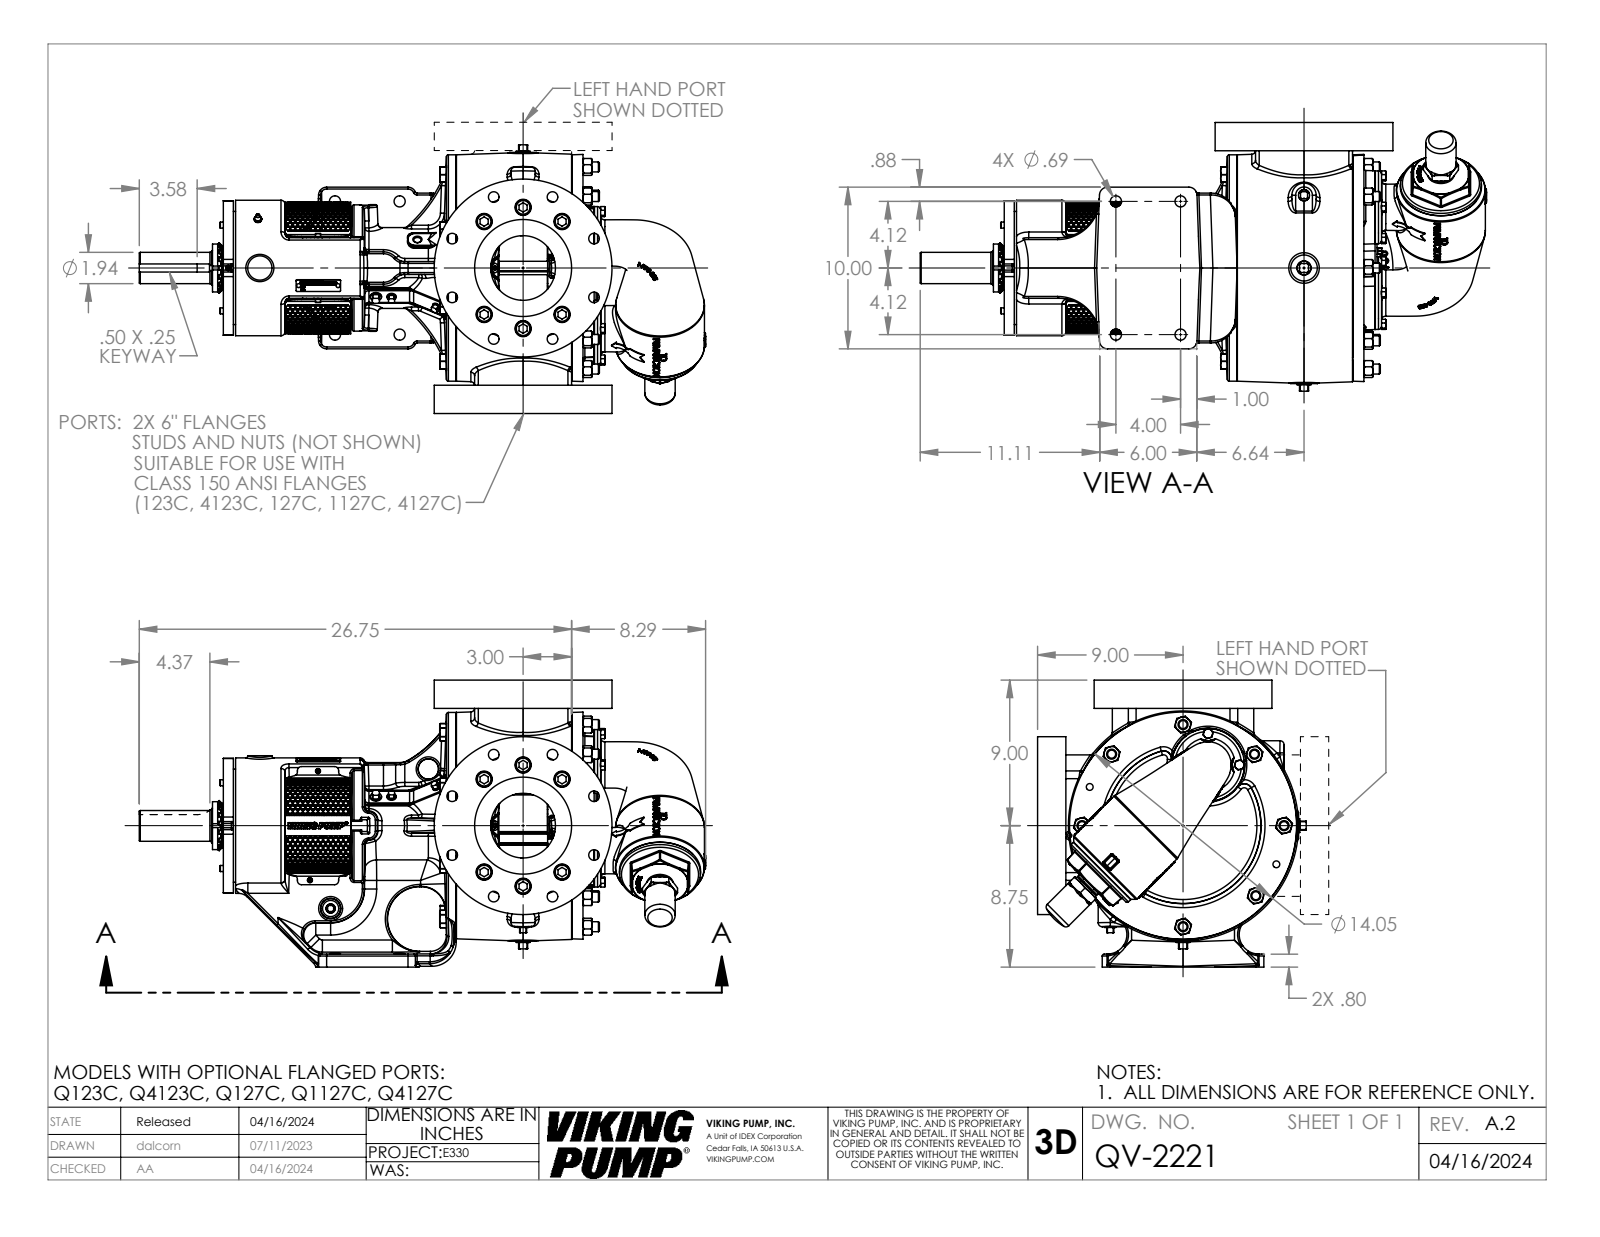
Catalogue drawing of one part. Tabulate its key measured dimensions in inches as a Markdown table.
| quantity | value |
| --- | --- |
| part name | QV-2221 |
| STEP written by | SolidWorks 2022 (AUTOMOTIVE_DESIGN) |
| units | inches |
| bodies | 1 solid, 4875 faces (1722 planar, 848 cylindrical, 2305 other) |
| overall size | 35.04 × 17.75 × 16.621 |
| volume | 2 453 in³ |
| surface area | 2 567 in² |
| round holes (diameter × count) | 0.656 × 16, 0.656 × 12, 1 × 12, 0.25 × 9, 0.266 × 8, 0.406 × 8, 0.41 × 8, 1.157 × 8, 0.688 × 4, 0.159 × 2, 0.313 × 2, 0.33 × 2 |
| round bosses / shafts (diameter × count) | 0.937 × 12, 0.625 × 9, 0.617 × 8, 0.375 × 8, 0.625 × 3, 0.312 × 3, 0.19 × 3, 11 × 2 |
| partial cylindrical surfaces (radius × count) | 0.12 × 60, 0.06 × 34, 0.25 × 30, 0.5 × 23, 0.015 × 18, 0.092 × 18, 0.07 × 16, 0.75 × 16 |
| main face-to-face distances | 1.75, 17.75, 16, 3.75, 0.5, 21.754, 22.254, 18.004, 18.504, 7.909 |
| hole center spacings | 3.75, 2.079, 3.635, 4.75, 6.718, 5.783, 1.628, 1.927 |
